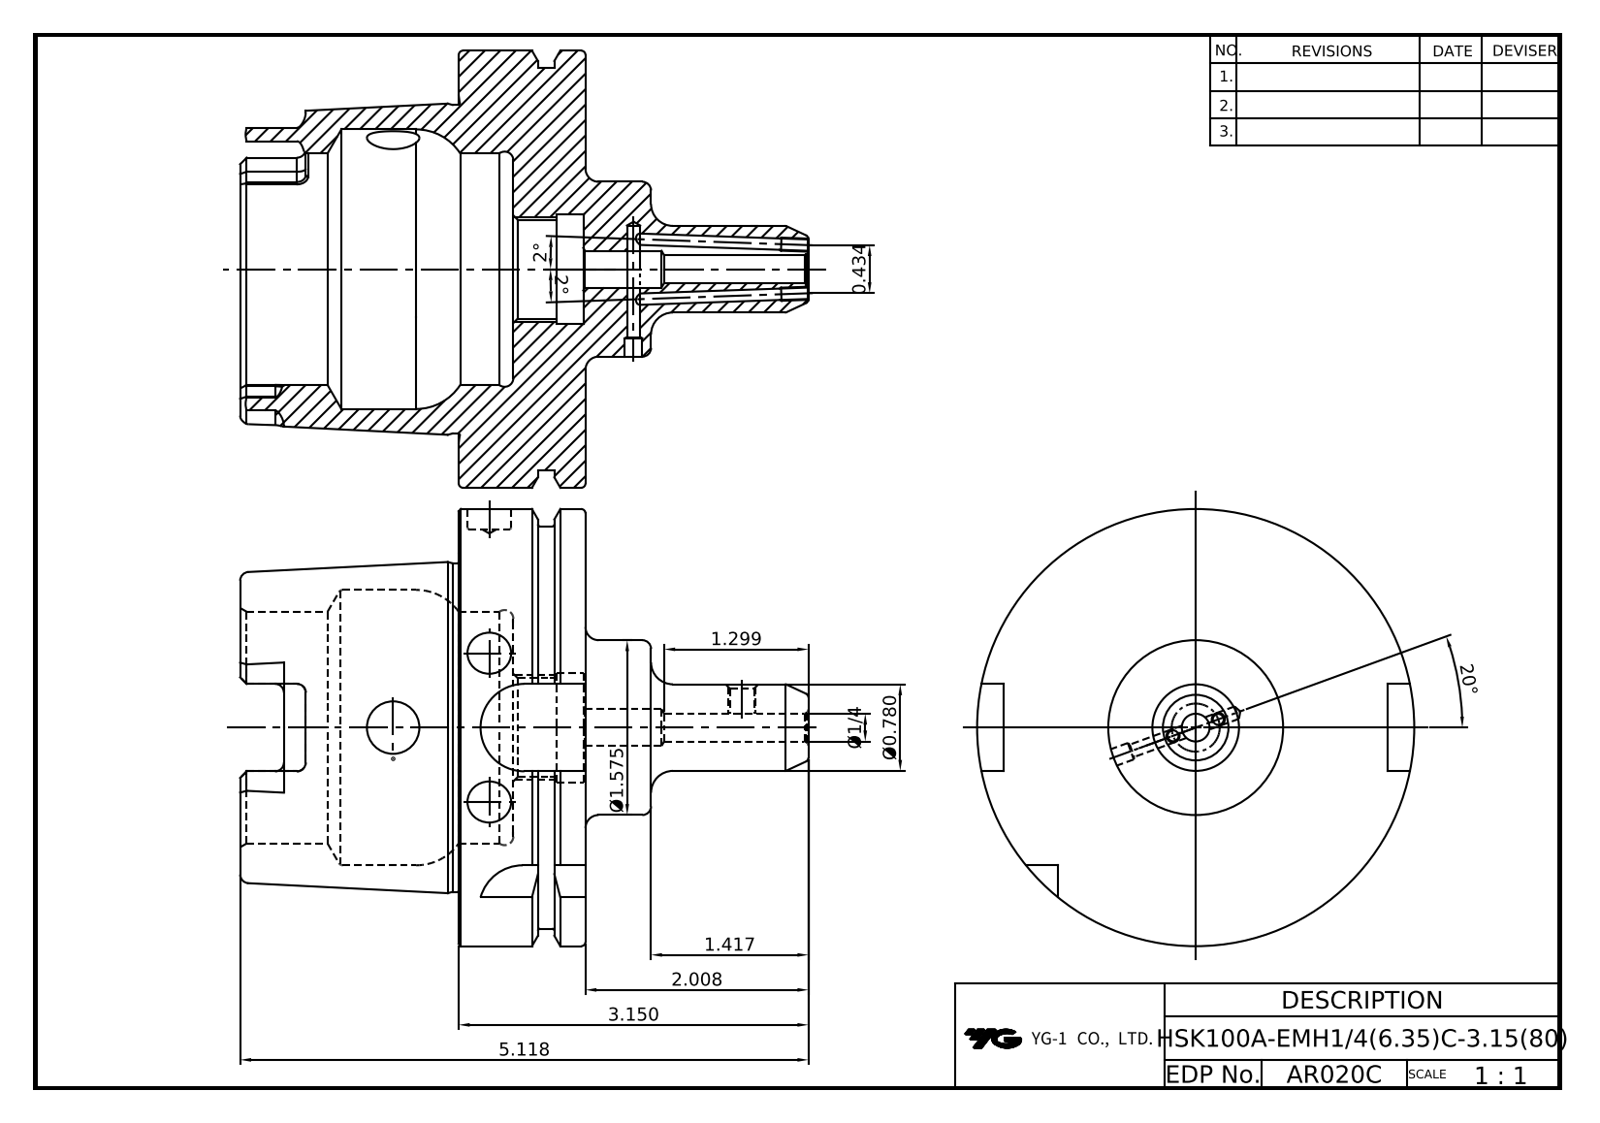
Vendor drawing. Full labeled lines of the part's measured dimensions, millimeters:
Part name (STEP PRODUCT): LO-HSK100A-EMH6.35C-80
STEP written by: Autodesk Inventor 2022 (AUTOMOTIVE_DESIGN)
Units: millimetres
Bodies: 1 solid, 133 faces (38 planar, 42 cylindrical, 53 other)
Overall size (bounding box): 129.99 × 100 × 100
Volume: 281 017 mm³ · Surface area: 55 338 mm²
Round holes (diameter × count): ⌀10 ×3, ⌀2.46 ×2, ⌀3 ×1, ⌀4 ×1, ⌀5.36 ×1, ⌀6.35 ×1, ⌀8.4 ×1, ⌀12 ×1, ⌀22.38 ×1, ⌀25 ×1, ⌀53 ×1, ⌀63 ×1
Round bosses / shafts (diameter × count): ⌀100 ×1, ⌀92 ×1, ⌀75.41 ×1, ⌀40 ×1, ⌀19.81 ×1
Partial cylindrical surfaces — rounded edges, fillets, slot ends (radius × count): R2 ×6, R4.88 ×4, R10 ×4
Main face-to-face distances: 29, 12.5, 16.5, 79, 62.5, 50, 15, 88, 78.5, 28.5
Hole centre spacings: 33, 57.8
